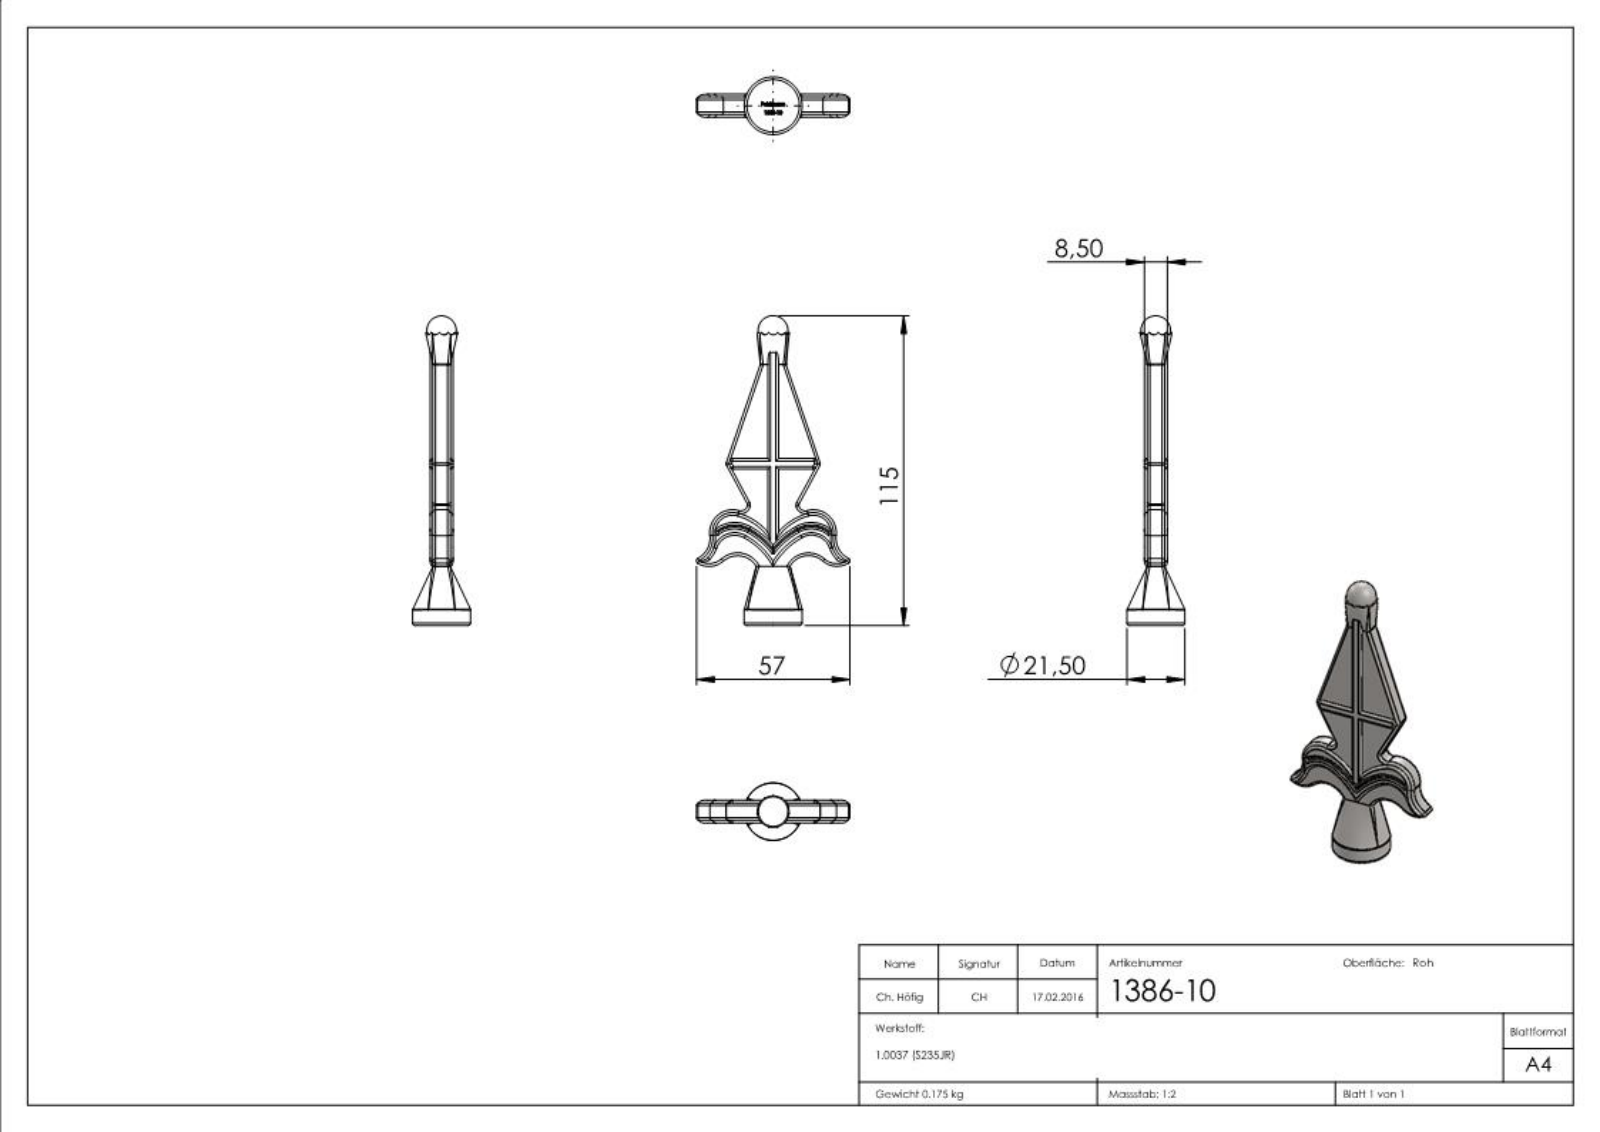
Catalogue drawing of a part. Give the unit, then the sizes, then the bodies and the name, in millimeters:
Units: millimetres
Overall size (bounding box): 115 × 57 × 21.5
Round bosses / shafts (diameter × count): ⌀21.5 ×1
Partial cylindrical surfaces — rounded edges, fillets, slot ends (radius × count): R1 ×38, R2.03 ×11, R8 ×4, R8.5 ×4, R2.5 ×2
Main face-to-face distances: 6.5, 1, 7.5, 8.5, 0.5, 2.97, 3.25, 0.39, 2.79, 1.26
Volume: 22 373 mm³ · Surface area: 8 417 mm²
Bodies: 1 solid, 449 faces (119 planar, 73 cylindrical, 257 other)
Part name (STEP PRODUCT): 1386-10
STEP written by: SolidWorks 2015 (CONFIG_CONTROL_DESIGN)
